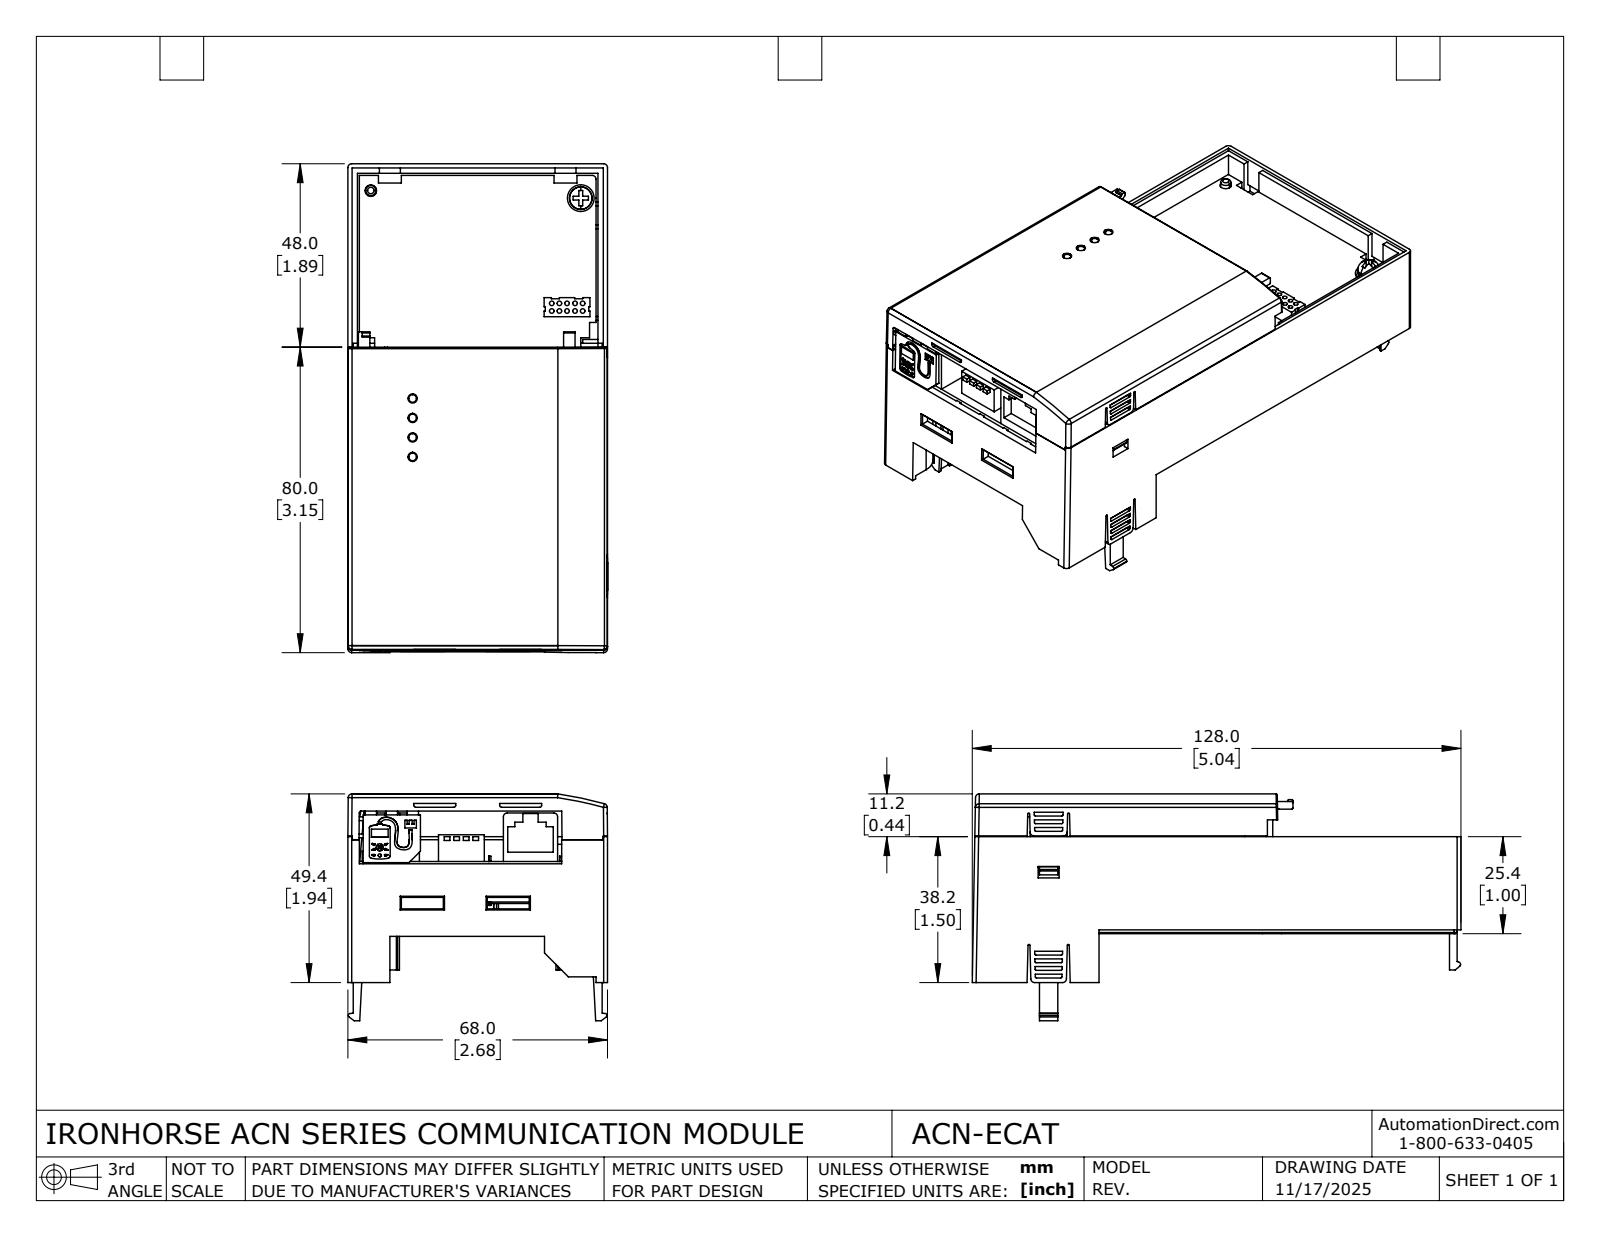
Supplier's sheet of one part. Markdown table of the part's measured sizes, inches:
| quantity | value |
| --- | --- |
| part name | ACN-ECAT |
| STEP written by | SolidWorks 2024 (AUTOMOTIVE_DESIGN) |
| units | inches |
| bodies | 11 solids, 1964 faces (1329 planar, 503 cylindrical, 132 other) |
| overall size | 5.041 × 2.681 × 2.339 |
| volume | 5.017 in³ |
| surface area | 127.1 in² |
| round holes (diameter × count) | 0.055 × 24, 0.047 × 10, 0.087 × 6, 0.138 × 5, 0.098 × 2, 0.11 × 2, 0.118 × 1 |
| round bosses / shafts (diameter × count) | 0.02 × 24, 0.091 × 6, 0.276 × 4, 0.232 × 4, 0.118 × 4, 0.031 × 4, 0.315 × 2, 0.106 × 1 |
| partial cylindrical surfaces (radius × count) | 0.039 × 65, 0.012 × 45, 0.02 × 23, 0.005 × 6, 0.01 × 6, 0.028 × 6, 0.074 × 6, 0.157 × 5 |
| main face-to-face distances | 0.098, 0.878, 0.063, 0.118, 0.181, 0.28, 0.217, 2.577, 0.78, 0.976 |
| hole center spacings | 0.077, 0.717, 0.154, 0.64, 0.793, 0.11, 0.109, 0.155 |
